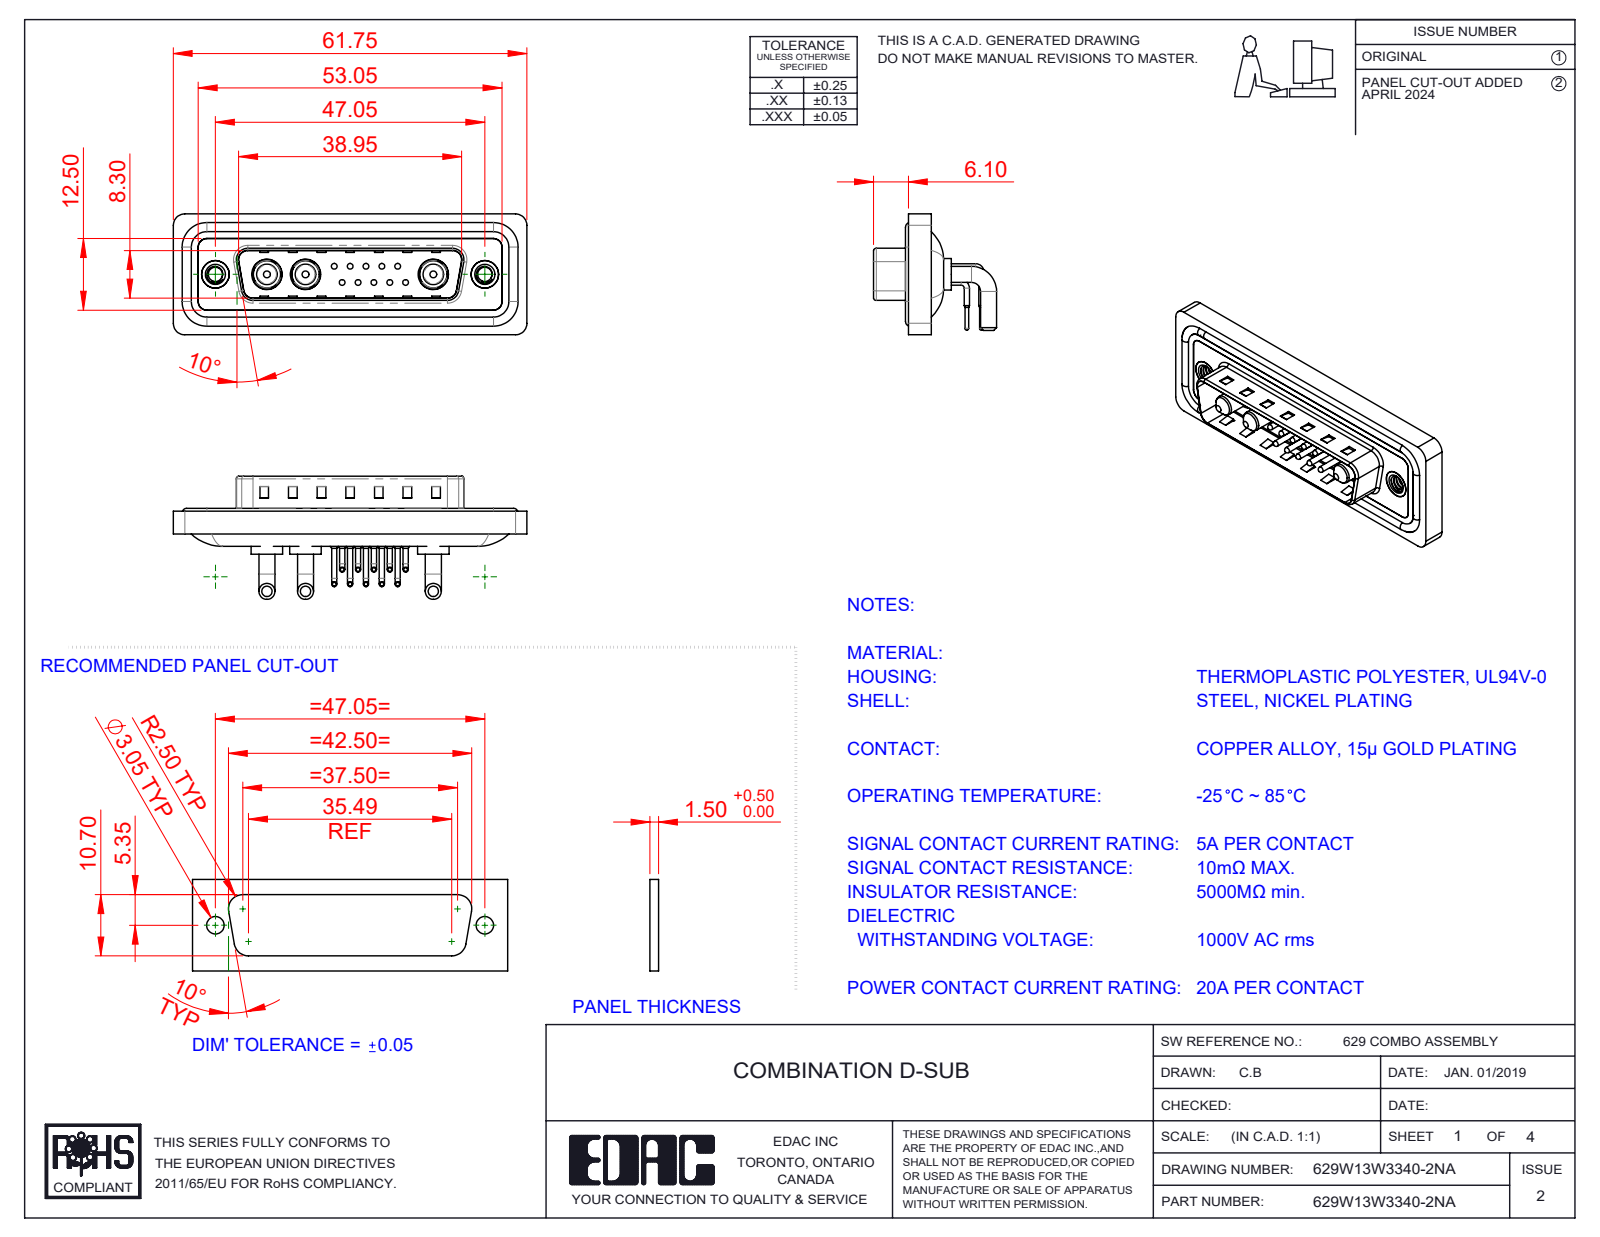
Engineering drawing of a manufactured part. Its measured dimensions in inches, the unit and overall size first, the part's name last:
Units: inches
Overall size (bounding box): 2.431 × 0.846 × 0.831
Round holes (diameter × count): ⌀0.03 ×10, ⌀0.063 ×10, ⌀0.079 ×10, ⌀0.191 ×3, ⌀0.209 ×3, ⌀0.098 ×2, ⌀0.157 ×2, ⌀0.189 ×2, ⌀0.197 ×2
Round bosses / shafts (diameter × count): ⌀0.035 ×20, ⌀0.059 ×10, ⌀0.039 ×10, ⌀0.026 ×10, ⌀0.11 ×6, ⌀0.063 ×4, ⌀0.217 ×3, ⌀0.205 ×3
Partial cylindrical surfaces — rounded edges, fillets, slot ends (radius × count): R0.059 ×18, R0.079 ×18, R0.04 ×10, R0.02 ×8, R0.063 ×8, R0.01 ×4, R0.024 ×4, R0.026 ×4
Main face-to-face distances: 0.016, 0.114, 0.031, 0.161, 0.043, 0.083, 0.063, 0.177, 0.059, 0.236
Hole centre spacings: 0.124, 0.109, 0.198, 0.218, 0.295, 0.198, 0.327, 0.398
Volume: 0.465 in³ · Surface area: 19.38 in²
Bodies: 23 solids, 1706 faces (879 planar, 609 cylindrical, 218 other)
Part name (STEP PRODUCT): 629W13W3340-2NA; 629Combo Contact Row 2; 629Combo Housing_13W3; 629Combo Threaded Rivet_A (+5 more)
STEP written by: SolidWorks 2023 (CONFIG_CONTROL_DESIGN)
